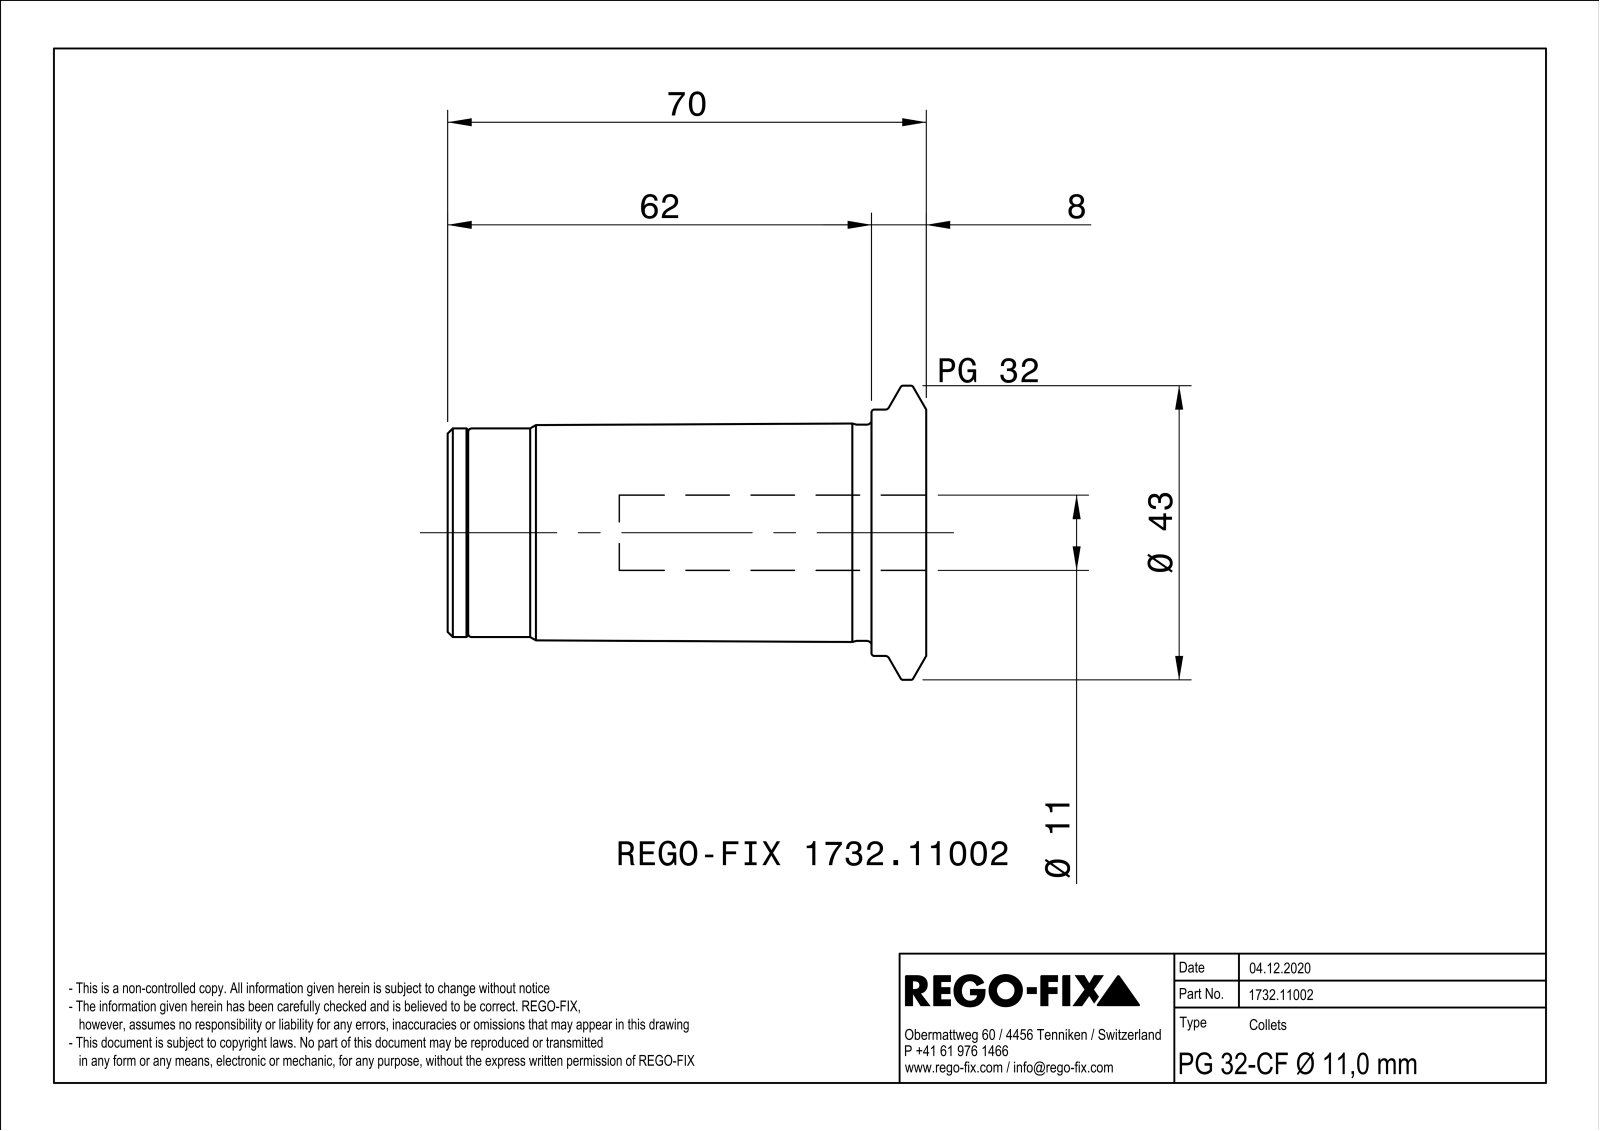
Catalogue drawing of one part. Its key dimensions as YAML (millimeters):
part_name: "NOCUT"
step_written_by: "SIEMENS PLM Software Solid Edge ST10 (AUTOMOTIVE_DESIGN)"
units: millimeters
bodies: {solids: 1, faces: 135, planar: 34, cylindrical: 46, other: 55}
overall_size: [70, 43, 42.99]
volume: 45949
surface_area: 16831
round_holes:
  - {diameter: 4, count: 3}
  - {diameter: 8.92, count: 1}
  - {diameter: 10.5, count: 1}
  - {diameter: 11, count: 1}
  - {diameter: 15.5, count: 1}
  - {diameter: 26.92, count: 1}
  - {diameter: 28.5, count: 1}
round_bosses_or_shafts:
  - {diameter: 43, count: 1}
  - {diameter: 36, count: 1}
  - {diameter: 31.6, count: 1}
  - {diameter: 30.5, count: 1}
  - {diameter: 26.5, count: 1}
  - {diameter: 21, count: 1}
partial_cylinders:
  - {radius: 2, count: 6}
  - {radius: 1, count: 3}
  - {radius: 3.5, count: 3}
  - {radius: 3.98, count: 1}
  - {radius: 4.75, count: 1}
  - {radius: 8.75, count: 1}
face_to_face_distances: [1, 70, 58, 12, 59, 11, 8, 60, 2, 10]
hole_center_spacings: [7.75, 13.42, 13.43]
